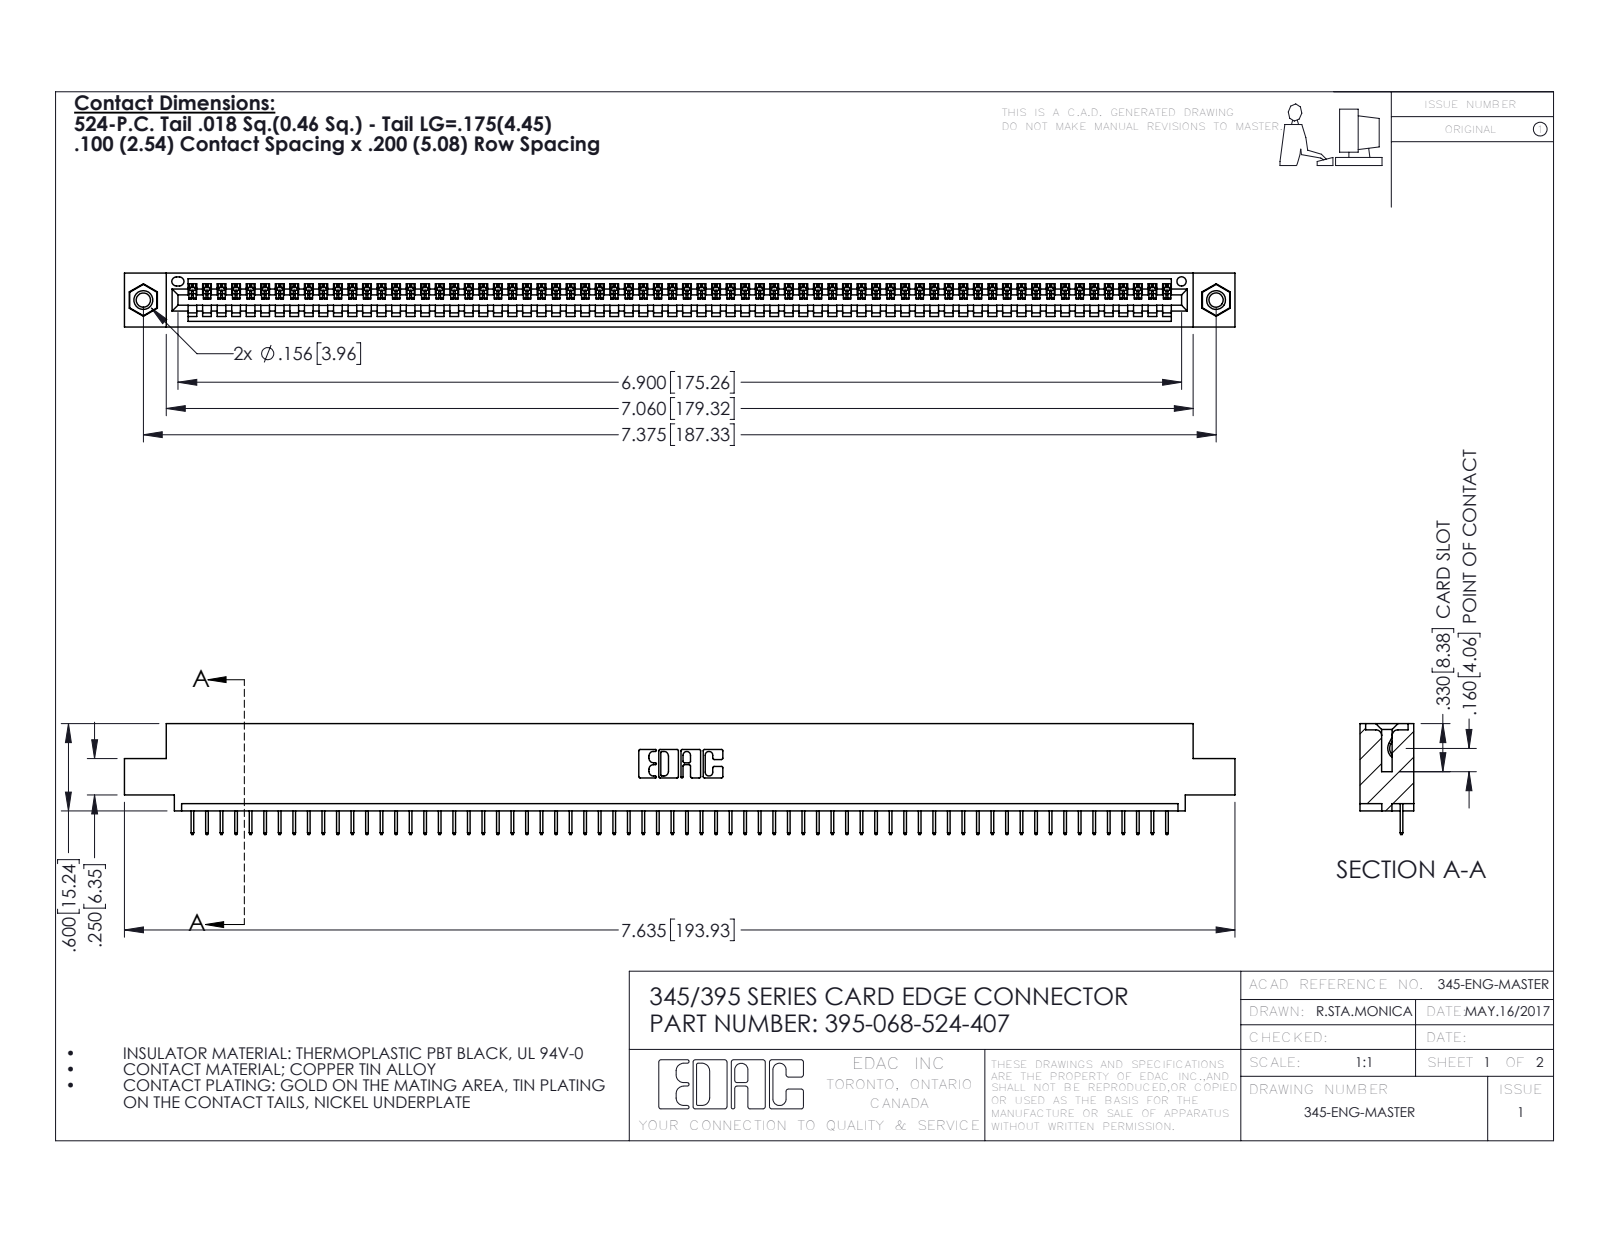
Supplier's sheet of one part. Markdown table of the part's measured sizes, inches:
| quantity | value |
| --- | --- |
| part name | 345-250-001_345-250-005-103; 395-068-524-407; 345 Part_0.110 Offset - 0.156 Dia-TI; 345-292-001_345-293-124 |
| STEP written by | SolidWorks 2016 (CONFIG_CONTROL_DESIGN) |
| units | inches |
| bodies | 71 solids, 4406 faces (3244 planar, 1146 cylindrical, 16 other) |
| overall size | 7.635 × 0.762 × 0.37 |
| volume | 1.115 in³ |
| surface area | 37.04 in² |
| round holes (diameter × count) | 0.098 × 2, 0.125 × 2, 0.156 × 2, 0.064 × 1 |
| round bosses / shafts (diameter × count) | 0.155 × 2 |
| partial cylindrical surfaces (radius × count) | 0.006 × 136, 0.01 × 22, 0.007 × 6, 0.031 × 6, 0.026 × 3, 0.031 × 2, 0.04 × 2, 0.014 × 1 |
| main face-to-face distances | 0.072, 0.298, 0.37, 0.2, 0.098, 0.272, 0.025, 0.225, 0.072, 0.149 |
| hole center spacings | 0.27, 7.139, 7.375 |
